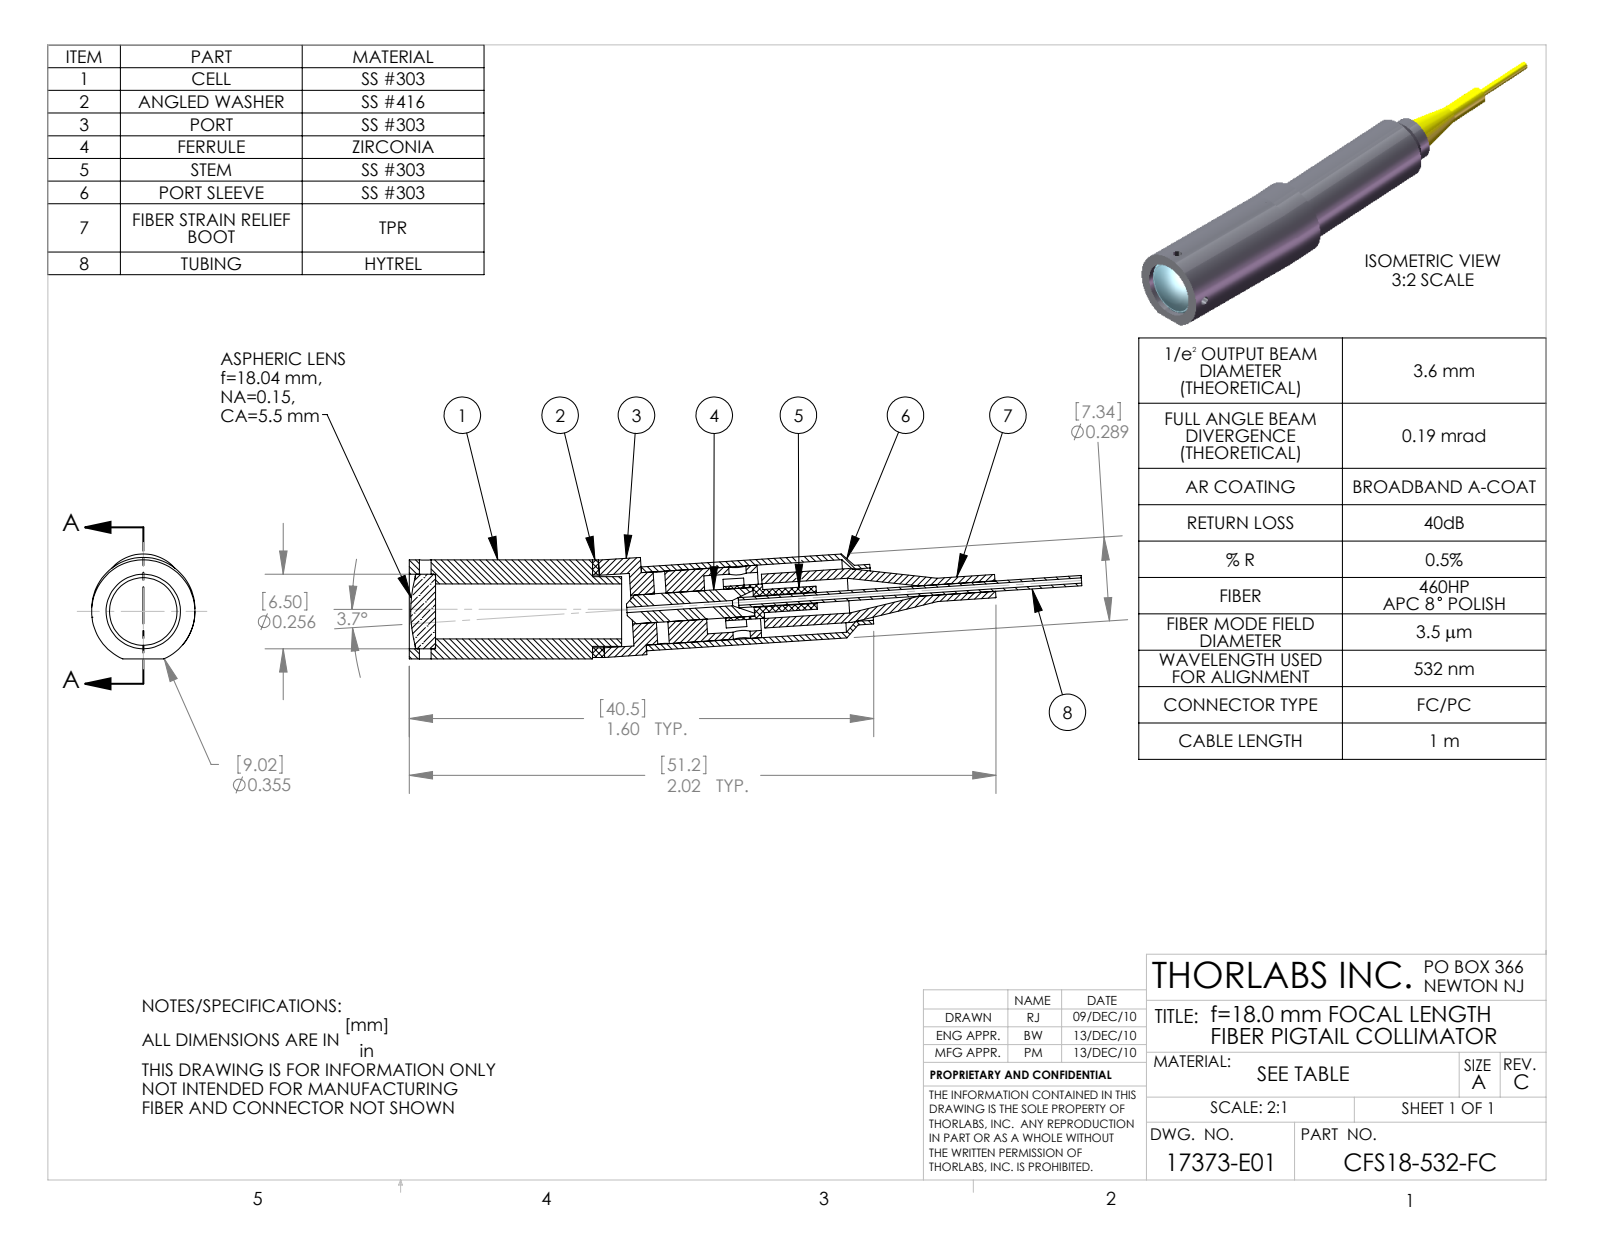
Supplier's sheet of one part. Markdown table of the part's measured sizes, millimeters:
| quantity | value |
| --- | --- |
| part name | 17373-E0W |
| STEP written by | SolidWorks 2009 (AUTOMOTIVE_DESIGN) |
| units | millimeters |
| bodies | 0 solids, 54 faces (13 planar, 31 cylindrical, 10 other) |
| overall size | 58.72 × 9.16 × 9.02 |
| round holes (diameter × count) | 1.02 × 2, 0.46 × 1, 4.57 × 1, 6.5 × 1 |
| round bosses / shafts (diameter × count) | 9.02 × 1, 9 × 1, 7.34 × 1, 5.21 × 1, 2.03 × 1, 0.9 × 1 |
| main face-to-face distances | 3.68, 16, 23.62, 19.94, 34.44, 30.76, 10.82, 15.49, 0.51, 41.98 |
